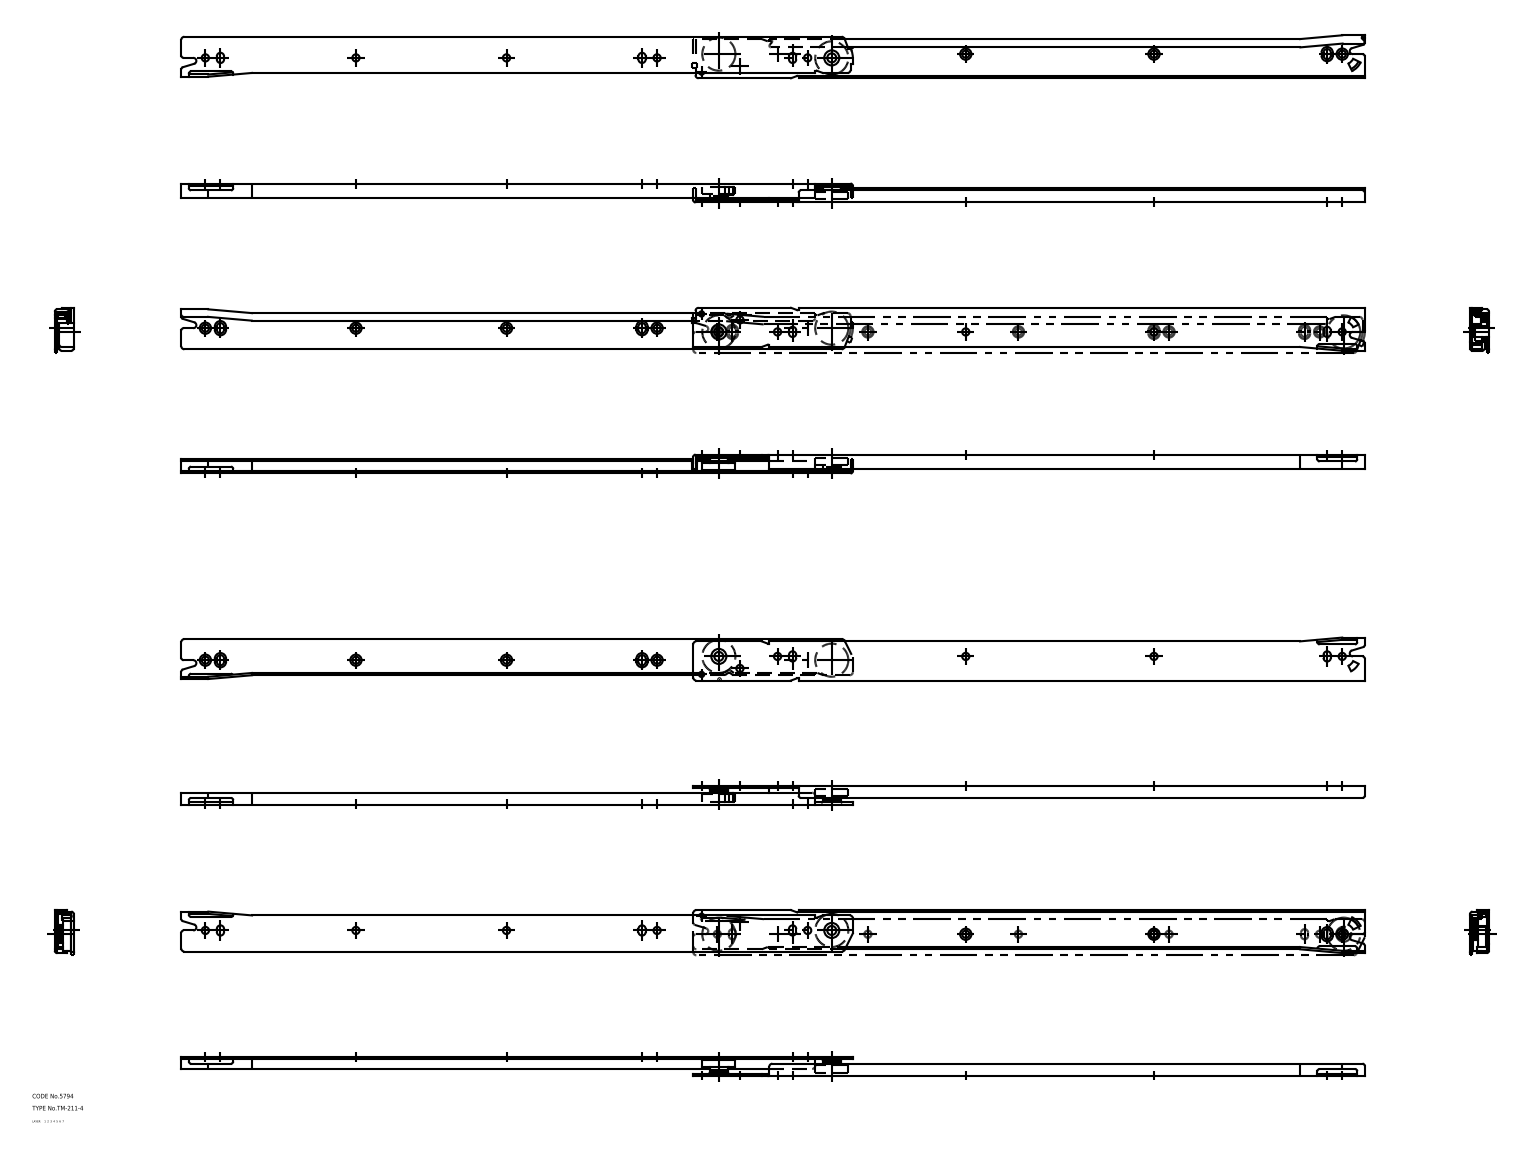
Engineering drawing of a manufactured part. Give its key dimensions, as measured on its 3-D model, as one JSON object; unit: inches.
{"part_name": "roller; member_B; member_A; TM_211_4_1188_36", "step_written_by": "CADfix (AUTOMOTIVE_DESIGN)", "units": "inches", "bodies": {"solids": 4, "faces": 183, "planar": 0, "cylindrical": 0, "other": 183}, "overall_size": [30.945, 1.122, 0.492], "volume_in3": 2.922, "surface_area_in2": 99.34}
